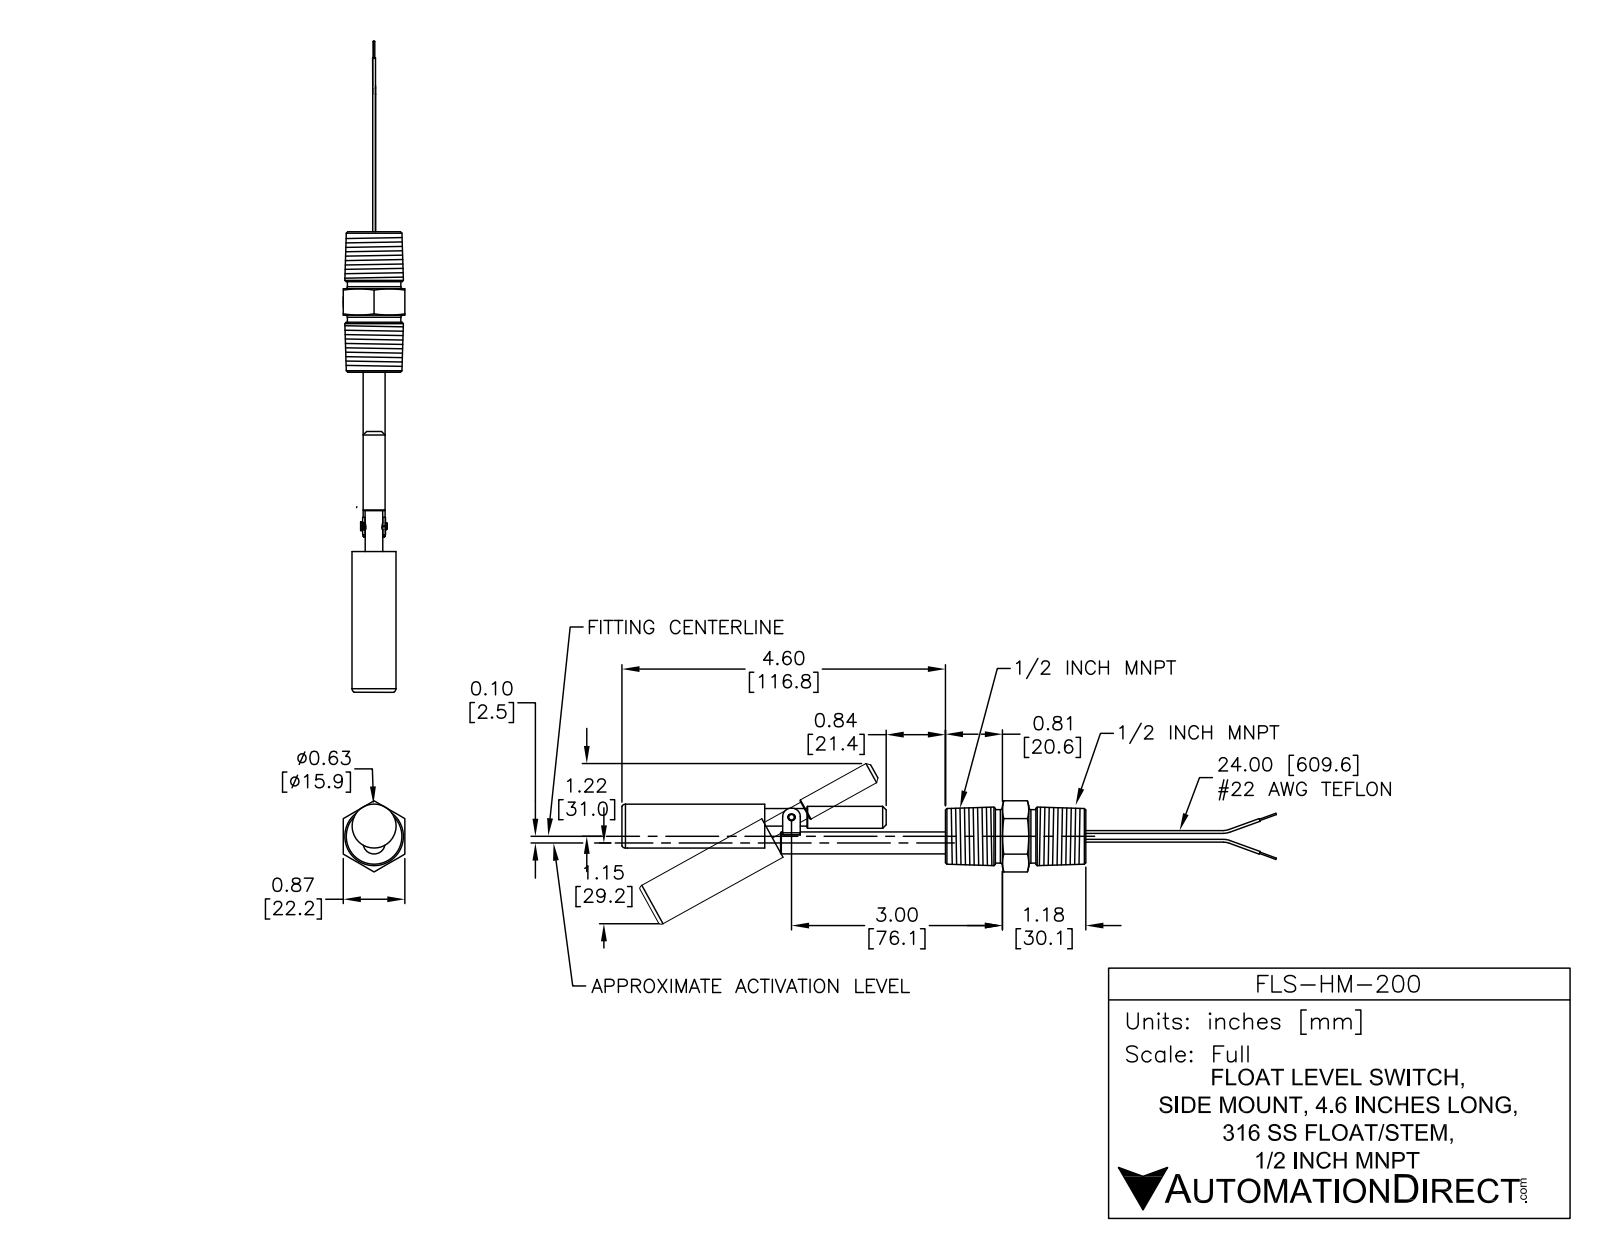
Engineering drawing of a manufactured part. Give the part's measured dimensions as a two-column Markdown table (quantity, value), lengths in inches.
| quantity | value |
| --- | --- |
| part name | FLS-HM-200 |
| STEP written by | SolidWorks 2013 (AUTOMOTIVE_DESIGN) |
| units | inches |
| bodies | 5 solids, 101 faces (33 planar, 36 cylindrical, 32 other) |
| overall size | 8.504 × 1.192 × 1 |
| volume | 2.021 in³ |
| surface area | 16.9 in² |
| round bosses / shafts (diameter × count) | 0.04 × 4, 0.02 × 2, 0.76 × 1, 0.68 × 1, 0.62 × 1, 0.32 × 1, 0.31 × 1, 0.25 × 1 |
| partial cylindrical surfaces (radius × count) | 0.005 × 2, 0.125 × 1, 0.156 × 1, 0.191 × 1 |
| main face-to-face distances | 1, 2, 4.585, 1.19, 0.81, 1.19, 0.38, 0.81, 3.775, 3.395 |
